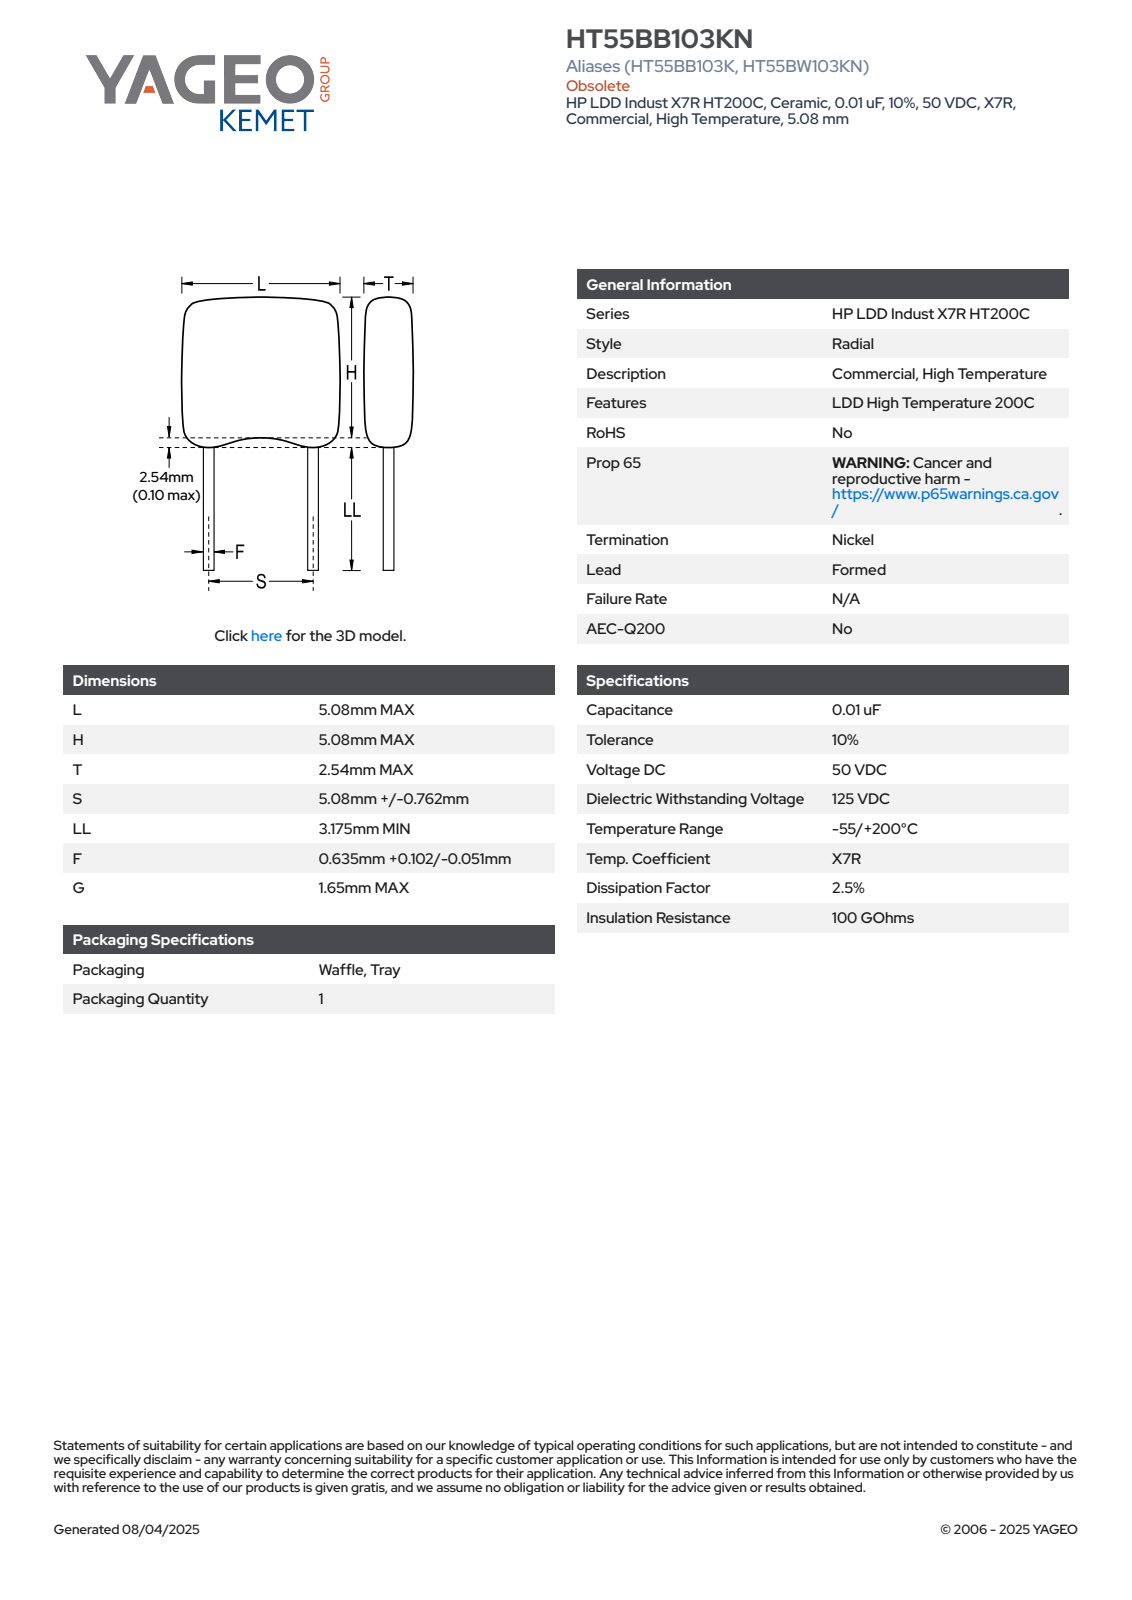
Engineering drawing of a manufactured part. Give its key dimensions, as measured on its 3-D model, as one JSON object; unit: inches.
{"part_name": "CCR_RMHS_HT55_L5.08H5.08T2.54S5.08LL31.75F0.635G1.65", "step_written_by": "SolidWorks 2014 (AUTOMOTIVE_DESIGN)", "units": "inches", "bodies": {"solids": 4, "faces": 73, "planar": 65, "cylindrical": 4, "other": 4}, "overall_size": [1.515, 0.225, 0.1], "volume_in3": 0.005, "surface_area_in2": 0.374, "round_bosses_or_shafts": [[0.025, 2]], "face_to_face_distances": [0.1, 0.2, 1.315, 1.515, 1.431, 0.116, 0.084, 1.399, 0.084, 0.032]}
